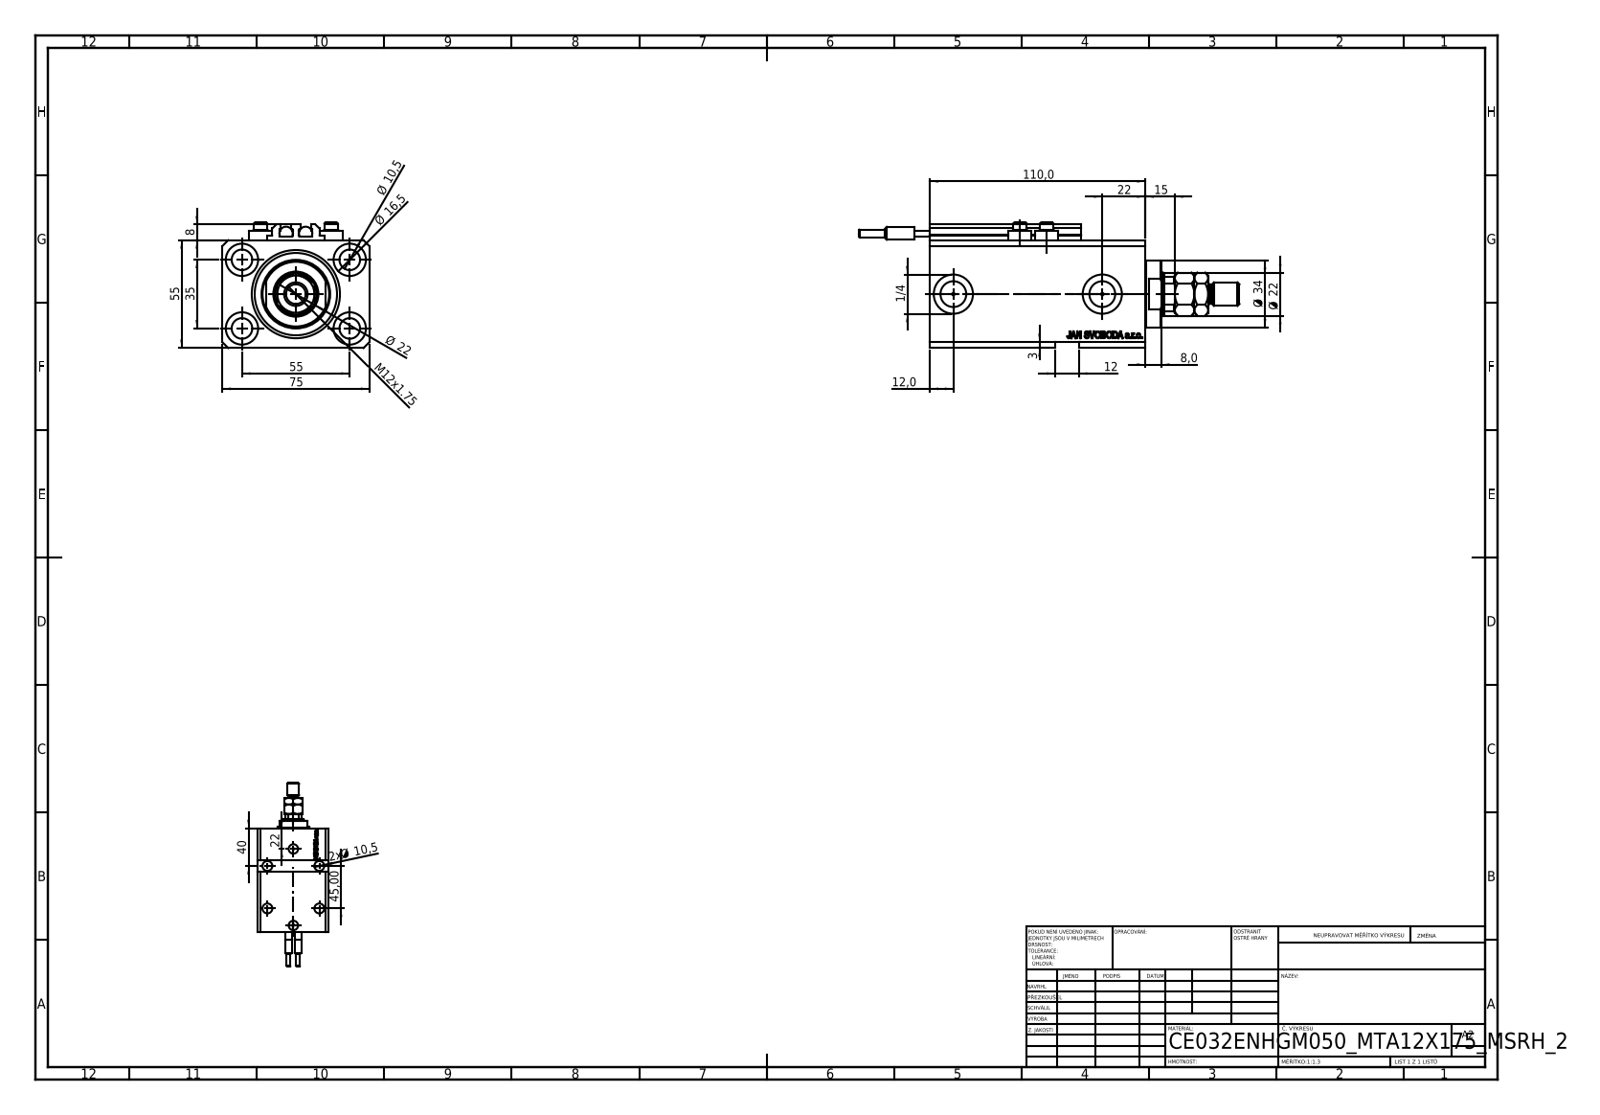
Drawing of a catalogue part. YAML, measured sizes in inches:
part_name: "V250CE_VC_E; ALLEN BOLT V250CE; MTA; SWITCH_V250CE (+2 more)"
step_written_by: "SolidWorks 2019 (CONFIG_CONTROL_DESIGN)"
units: inches
bodies: {solids: 11, faces: 1185, planar: 561, cylindrical: 162, other: 462}
overall_size: [7.638, 2.953, 2.52]
volume: 23.91
surface_area: 156.1
round_holes:
  - {diameter: 0.413, count: 9}
  - {diameter: 0.049, count: 4}
  - {diameter: 0.157, count: 4}
  - {diameter: 0.65, count: 4}
  - {diameter: 0.394, count: 2}
  - {diameter: 0.518, count: 2}
  - {diameter: 0.787, count: 2}
  - {diameter: 0.866, count: 1}
  - {diameter: 1.26, count: 1}
  - {diameter: 1.772, count: 1}
round_bosses_or_shafts:
  - {diameter: 0.457, count: 4}
  - {diameter: 0.276, count: 4}
  - {diameter: 0.268, count: 2}
  - {diameter: 0.256, count: 2}
  - {diameter: 0.157, count: 2}
  - {diameter: 1.339, count: 1}
  - {diameter: 0.472, count: 1}
  - {diameter: 0.394, count: 1}
partial_cylinders:
  - {radius: 0.008, count: 10}
  - {radius: 0.413, count: 1}
face_to_face_distances: [2.165, 2.953, 0.591, 0.118, 4.331, 2.244, 3.74, 0.39, 3.35, 3.941]
hole_center_spacings: [1.283, 1.294, 2.165, 2.706, 0.535, 0.555, 0.907, 1.016]
